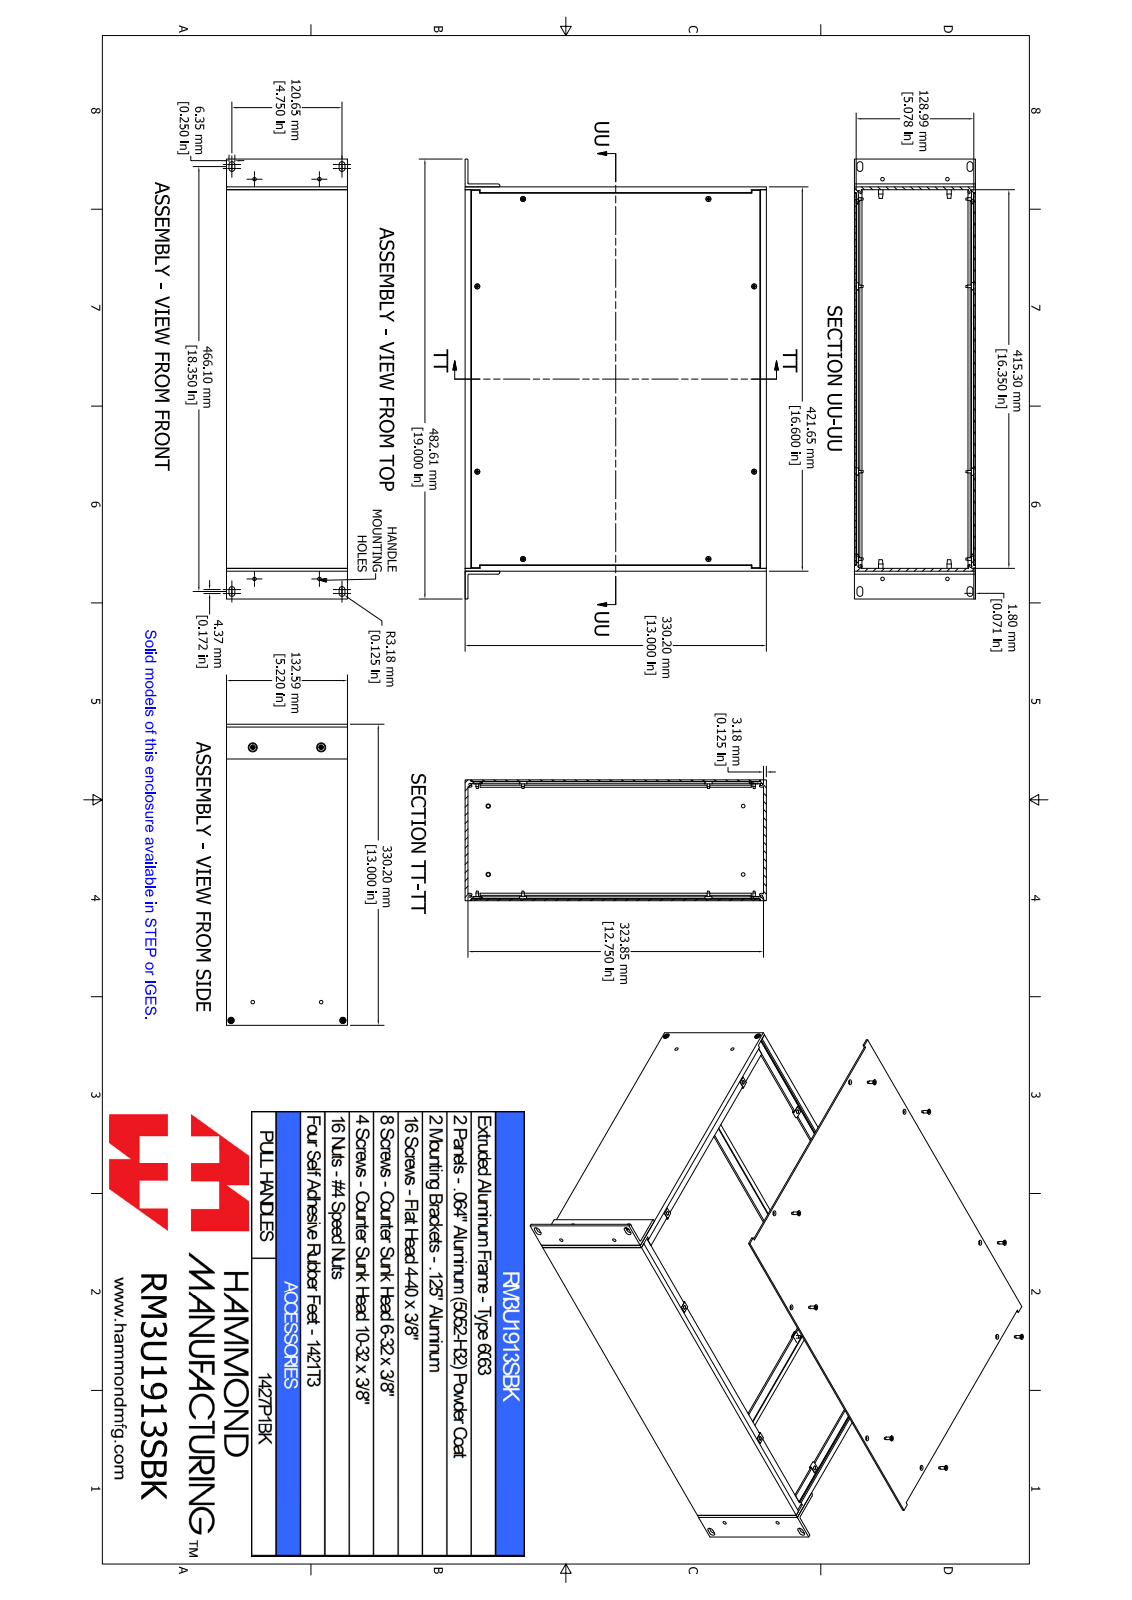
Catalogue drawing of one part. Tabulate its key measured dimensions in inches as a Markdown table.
| quantity | value |
| --- | --- |
| part name | RM3U1913SBK |
| STEP written by | SolidWorks 2021 (AUTOMOTIVE_DESIGN) |
| units | inches |
| bodies | 52 solids, 1352 faces (636 planar, 220 cylindrical, 496 other) |
| overall size | 19 × 13 × 5.22 |
| volume | 77.67 in³ |
| surface area | 1 663 in² |
| round holes (diameter × count) | 0.098 × 8, 0.118 × 8, 0.157 × 8, 0.169 × 8, 0.138 × 4, 0.156 × 4, 0.157 × 4, 0.217 × 2 |
| round bosses / shafts (diameter × count) | 0.214 × 8, 0.112 × 8, 0.238 × 4, 0.138 × 4, 0.333 × 2, 0.19 × 2 |
| partial cylindrical surfaces (radius × count) | 0.039 × 21, 0.125 × 16, 0.049 × 15, 0.037 × 8, 0.05 × 8, 0.038 × 4, 0.079 × 2 |
| main face-to-face distances | 0.071, 5.149, 5.22, 5.078, 0.125, 0.125, 16.6, 13, 12.875, 12.875 |
| hole center spacings | 8, 10.662, 11.827, 12.415, 1.224, 1.224, 2.8, 2.953 |
